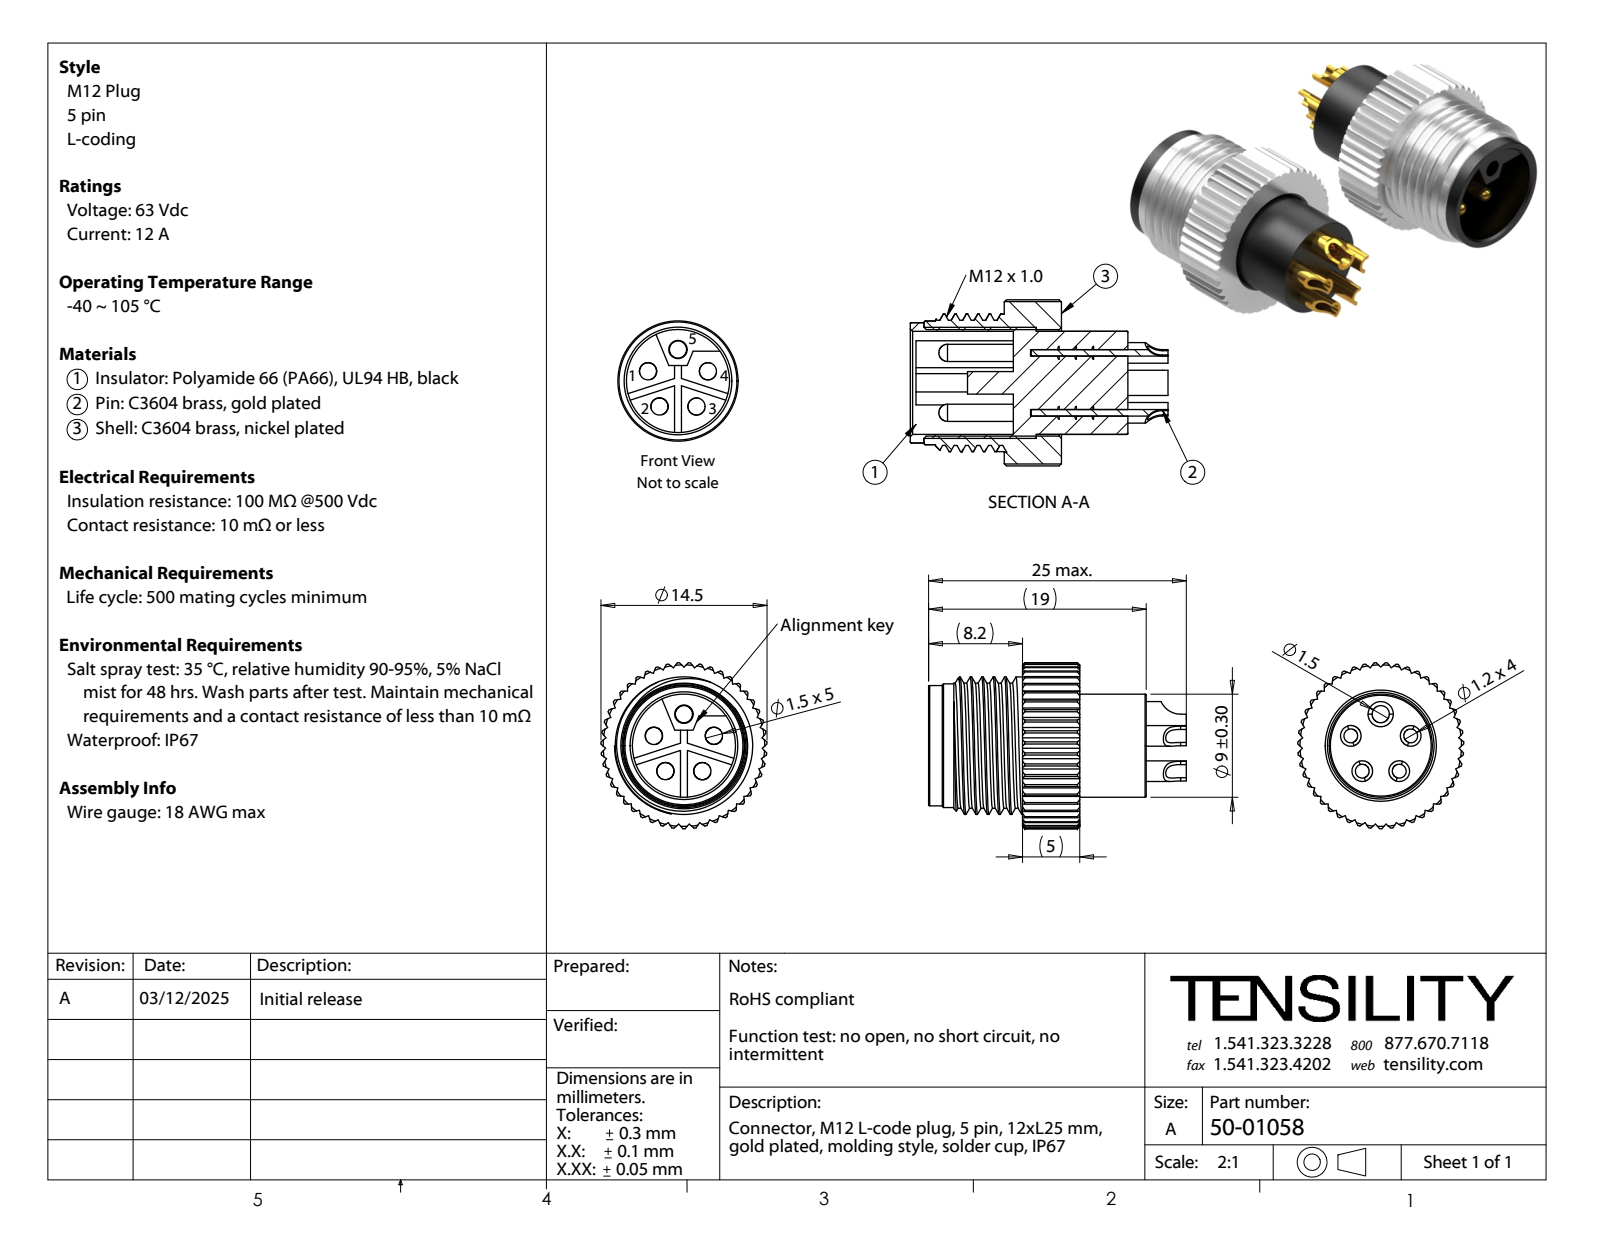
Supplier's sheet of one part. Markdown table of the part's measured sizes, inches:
| quantity | value |
| --- | --- |
| part name | 50-01058-03; 50-01058-04; 50-01058-01; 50-01058 (+1 more) |
| STEP written by | SolidWorks 2021 (CONFIG_CONTROL_DESIGN) |
| units | inches |
| bodies | 7 solids, 261 faces (73 planar, 109 cylindrical, 79 other) |
| overall size | 0.886 × 0.571 × 0.571 |
| volume | 0.1 in³ |
| surface area | 4.979 in² |
| round holes (diameter × count) | 0.059 × 5, 0.047 × 4, 0.063 × 1, 0.354 × 1, 0.366 × 1 |
| round bosses / shafts (diameter × count) | 0.071 × 4, 0.571 × 1, 0.472 × 1, 0.425 × 1, 0.413 × 1, 0.382 × 1, 0.087 × 1 |
| partial cylindrical surfaces (radius × count) | 0.067 × 2, 0.073 × 1 |
| main face-to-face distances | 0.197, 0.024, 0.228, 0.425, 0.394, 0.031, 0.165, 0.276, 0.472, 0.307 |
| hole center spacings | 0.108, 0.206, 0.128, 0.127, 0.206 |
